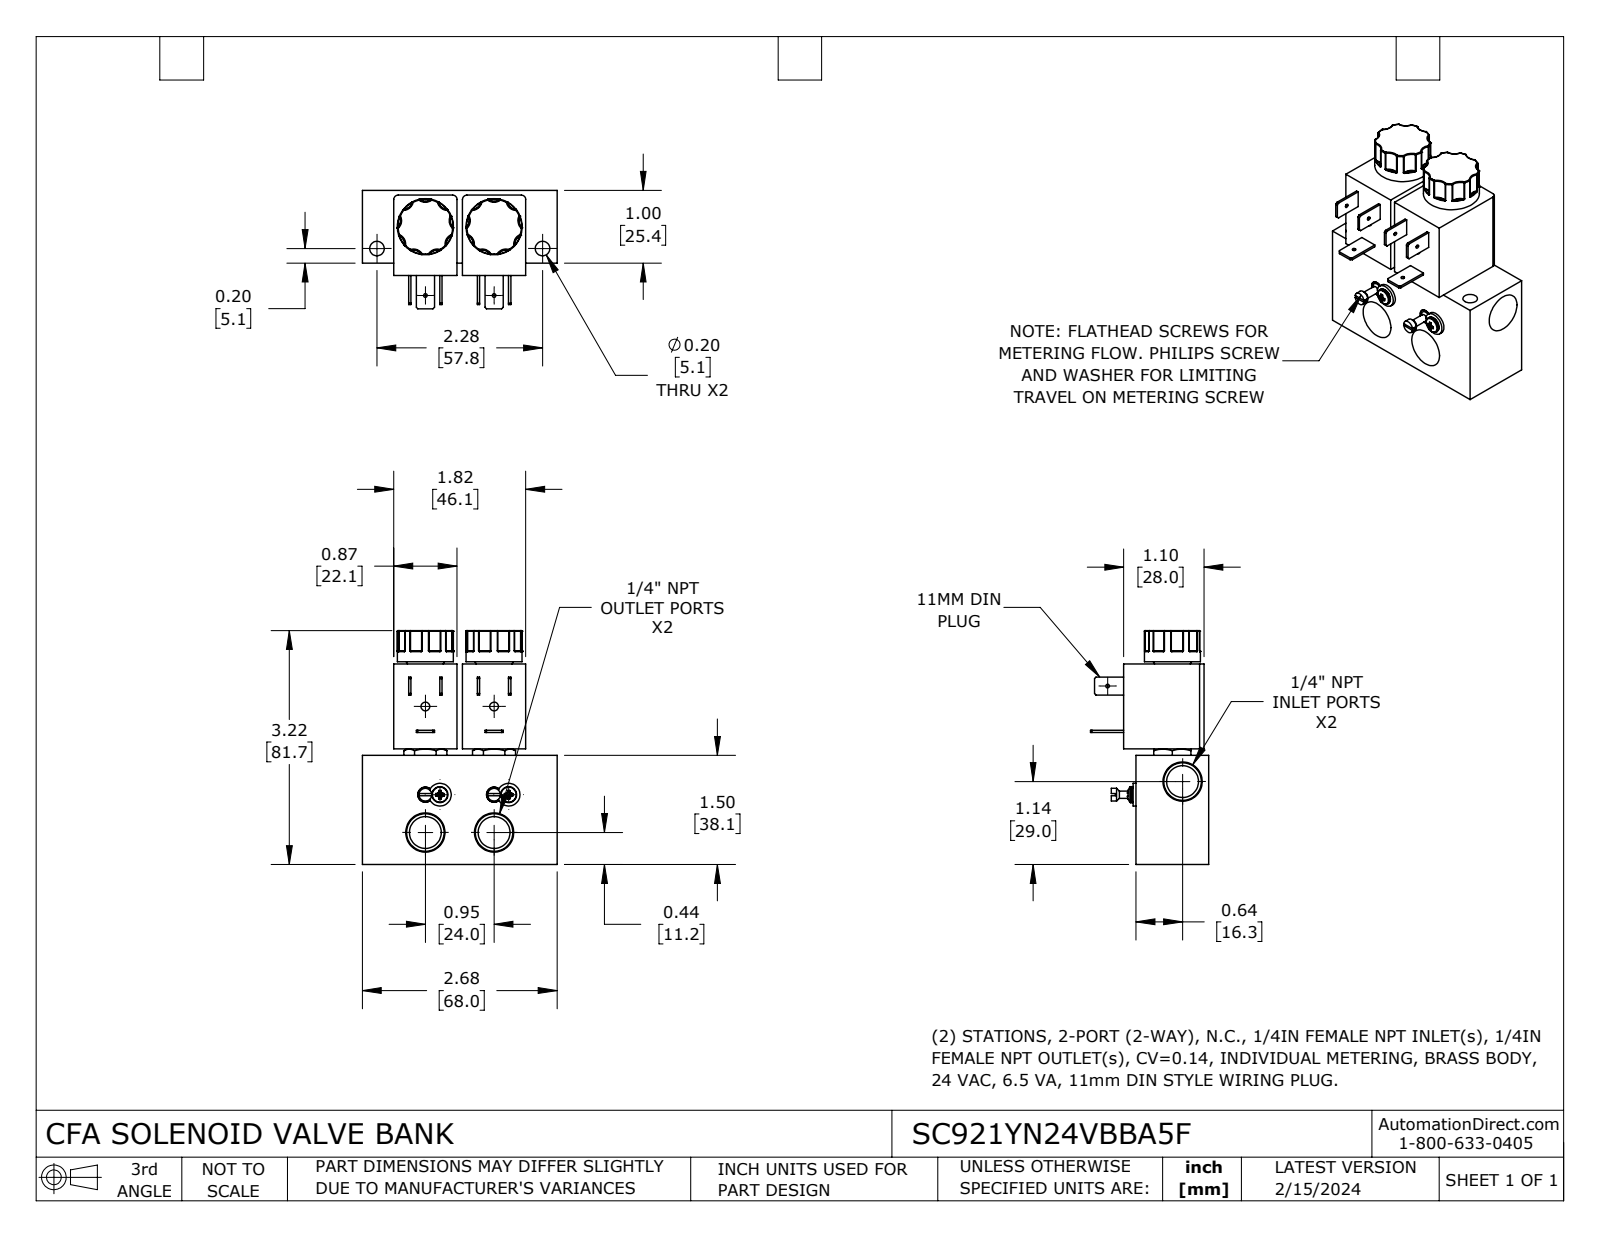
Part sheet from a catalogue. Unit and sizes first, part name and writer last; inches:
Units: inches
Overall size (bounding box): 3.215 × 2.677 × 1.627
Round holes (diameter × count): ⌀0.05 ×3, ⌀0.438 ×3, ⌀0.12 ×2, ⌀0.2 ×2, ⌀0.208 ×2
Round bosses / shafts (diameter × count): ⌀0.77 ×2, ⌀0.312 ×2, ⌀0.219 ×2, ⌀0.206 ×2, ⌀0.175 ×2, ⌀0.102 ×2, ⌀0.1 ×2
Partial cylindrical surfaces — rounded edges, fillets, slot ends (radius × count): R0.01 ×36, R0.133 ×18, R0.06 ×4, R0.308 ×1
Main face-to-face distances: 1, 0.945, 0.431, 1.301, 1.376, 2.246, 0.87, 1.5, 1.169, 0.169
Hole centre spacings: 0.945, 0.52, 0.928, 1.078, 1.212, 1.537, 1.732, 1.735
Volume: 6.159 in³ · Surface area: 40.27 in²
Bodies: 1 solid, 589 faces (156 planar, 152 cylindrical, 281 other)
Part name (STEP PRODUCT): SC921YN24VBBA5F
STEP written by: SolidWorks 2023 (CONFIG_CONTROL_DESIGN)
